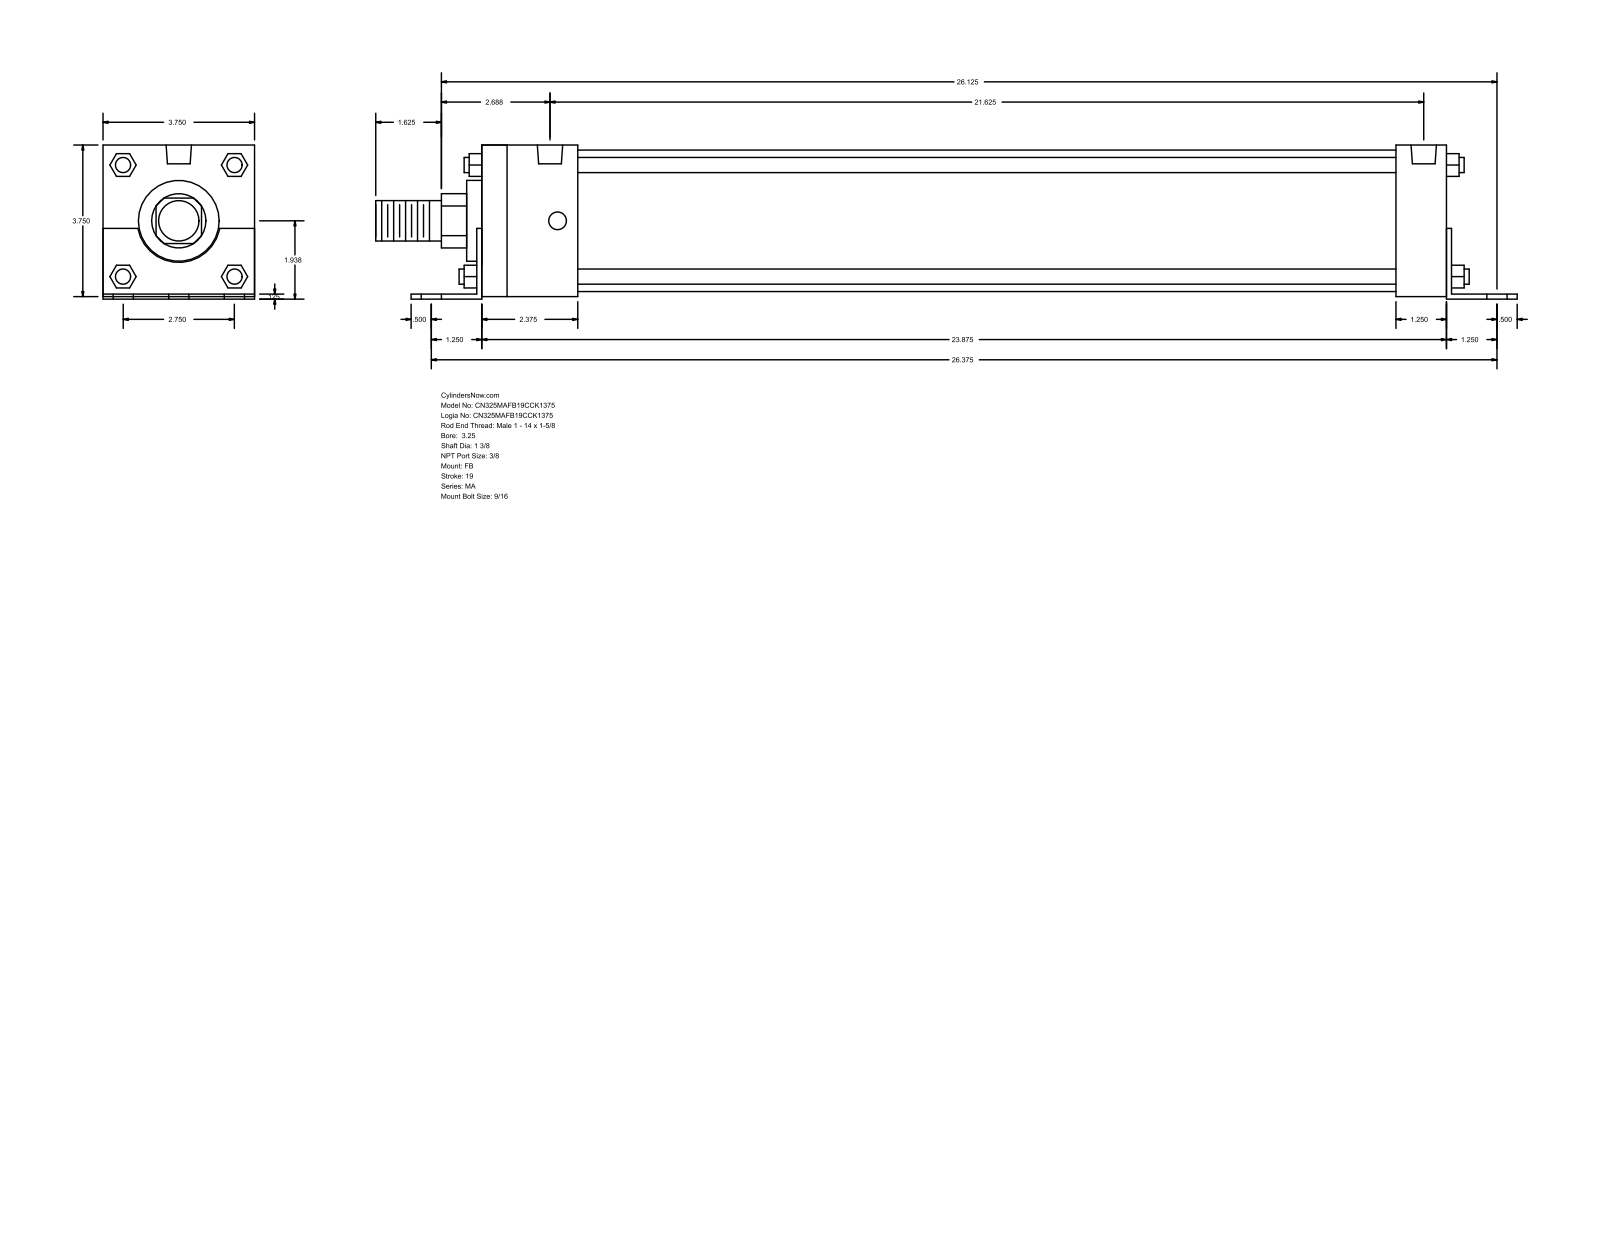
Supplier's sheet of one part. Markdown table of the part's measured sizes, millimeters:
| quantity | value |
| --- | --- |
| part name | MA_FB__0325_1.375 |
| STEP written by | GSSL Pune (CONFIG_CONTROL_DESIGN) |
| units | millimeters |
| bodies | 0 solids, 140 faces (105 planar, 35 cylindrical, 0 other) |
| overall size | 717.55 × 96.84 × 95.25 |
| round holes (diameter × count) | 14.29 × 6, 11.11 × 4, 15.93 × 2 |
| round bosses / shafts (diameter × count) | 9.53 × 4, 88.9 × 1, 50.8 × 1, 34.92 × 1, 25.4 × 1 |
| partial cylindrical surfaces (radius × count) | 17.06 × 1, 26.16 × 1 |
| main face-to-face distances | 95.24, 3.17, 1.59, 96.83, 1.58, 93.66, 609.6, 606.43, 31.75, 34.92 |
| hole center spacings | 34.92, 670.84, 669.93, 4.77, 57.78, 61.65, 69.84, 82.38 |
